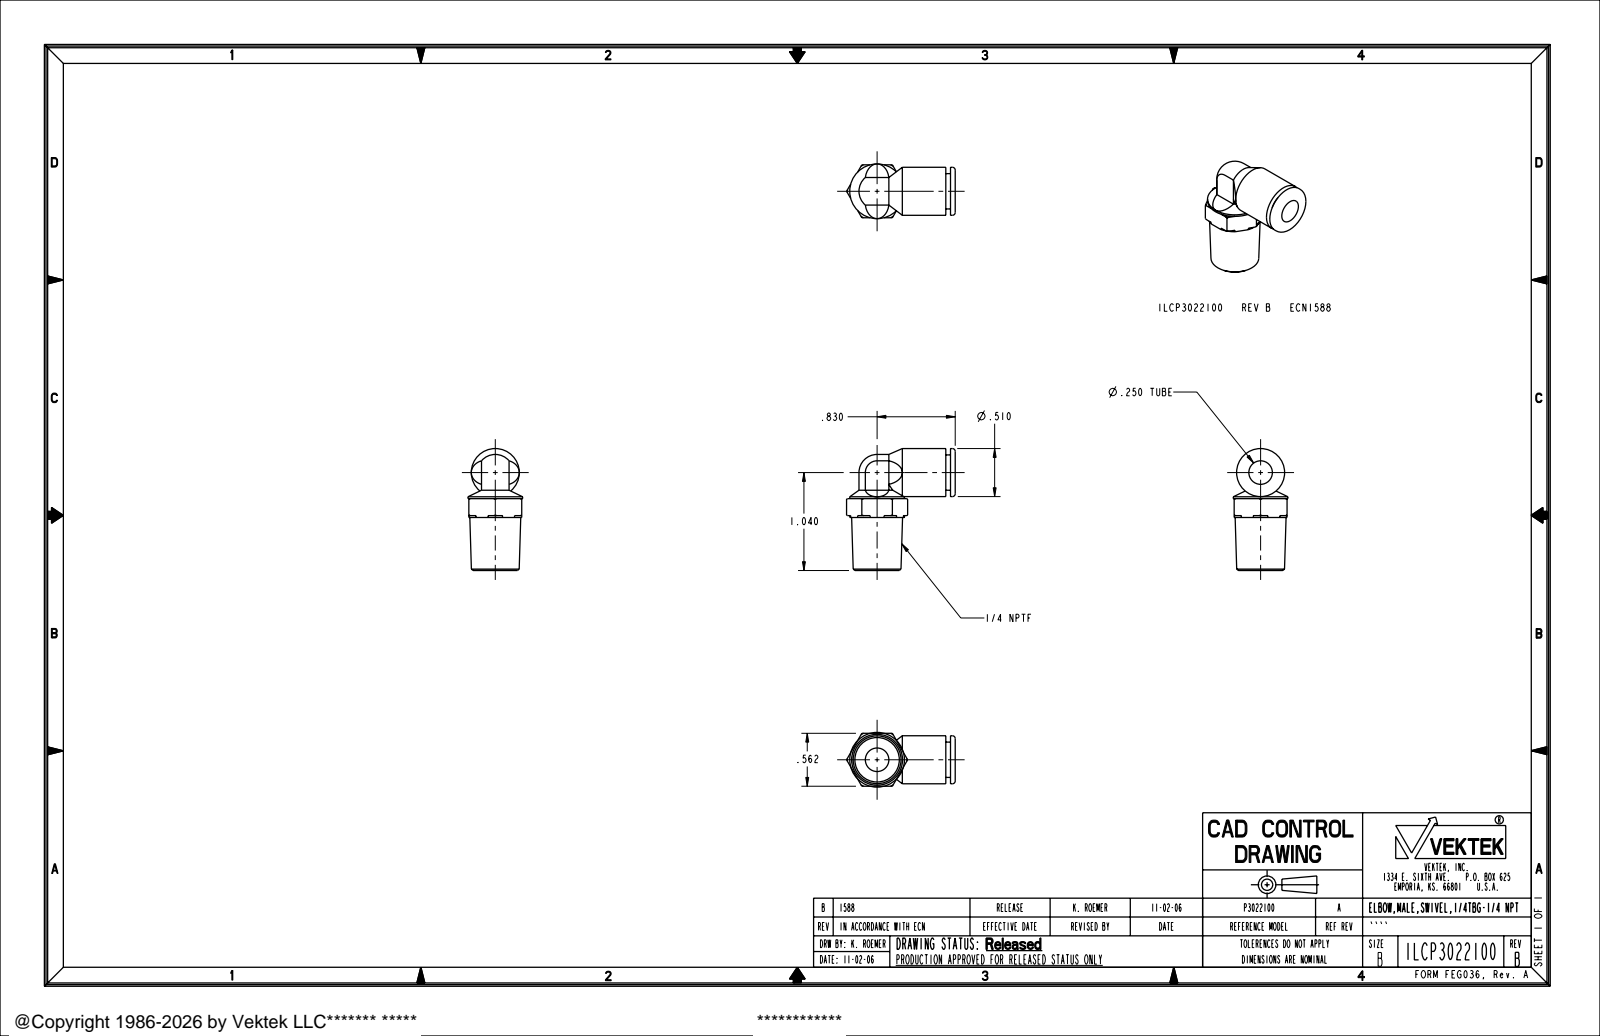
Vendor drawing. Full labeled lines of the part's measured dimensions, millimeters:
Part name (STEP PRODUCT): ILCP3022100
STEP written by: PRO/ENGINEER BY PARAMETRIC TECHNOLOGY CORPORATION, 2005180 (AUTOMOTIVE_DESIGN_CC2)
Units: millimetres
Bodies: 1 solid, 82 faces (35 planar, 22 cylindrical, 25 other)
Overall size (bounding box): 32.9 × 29.3 × 14.8
Volume: 4 310 mm³ · Surface area: 3 175 mm²
Round holes (diameter × count): ⌀6.4 ×2
Round bosses / shafts (diameter × count): ⌀14.8 ×1, ⌀13 ×1, ⌀9.5 ×1
Partial cylindrical surfaces — rounded edges, fillets, slot ends (radius × count): R4.9 ×2
Main face-to-face distances: 1.3, 14.3, 3.4, 10.9, 2.5, 7.4, 14.3, 19.4, 5.1, 14.8
